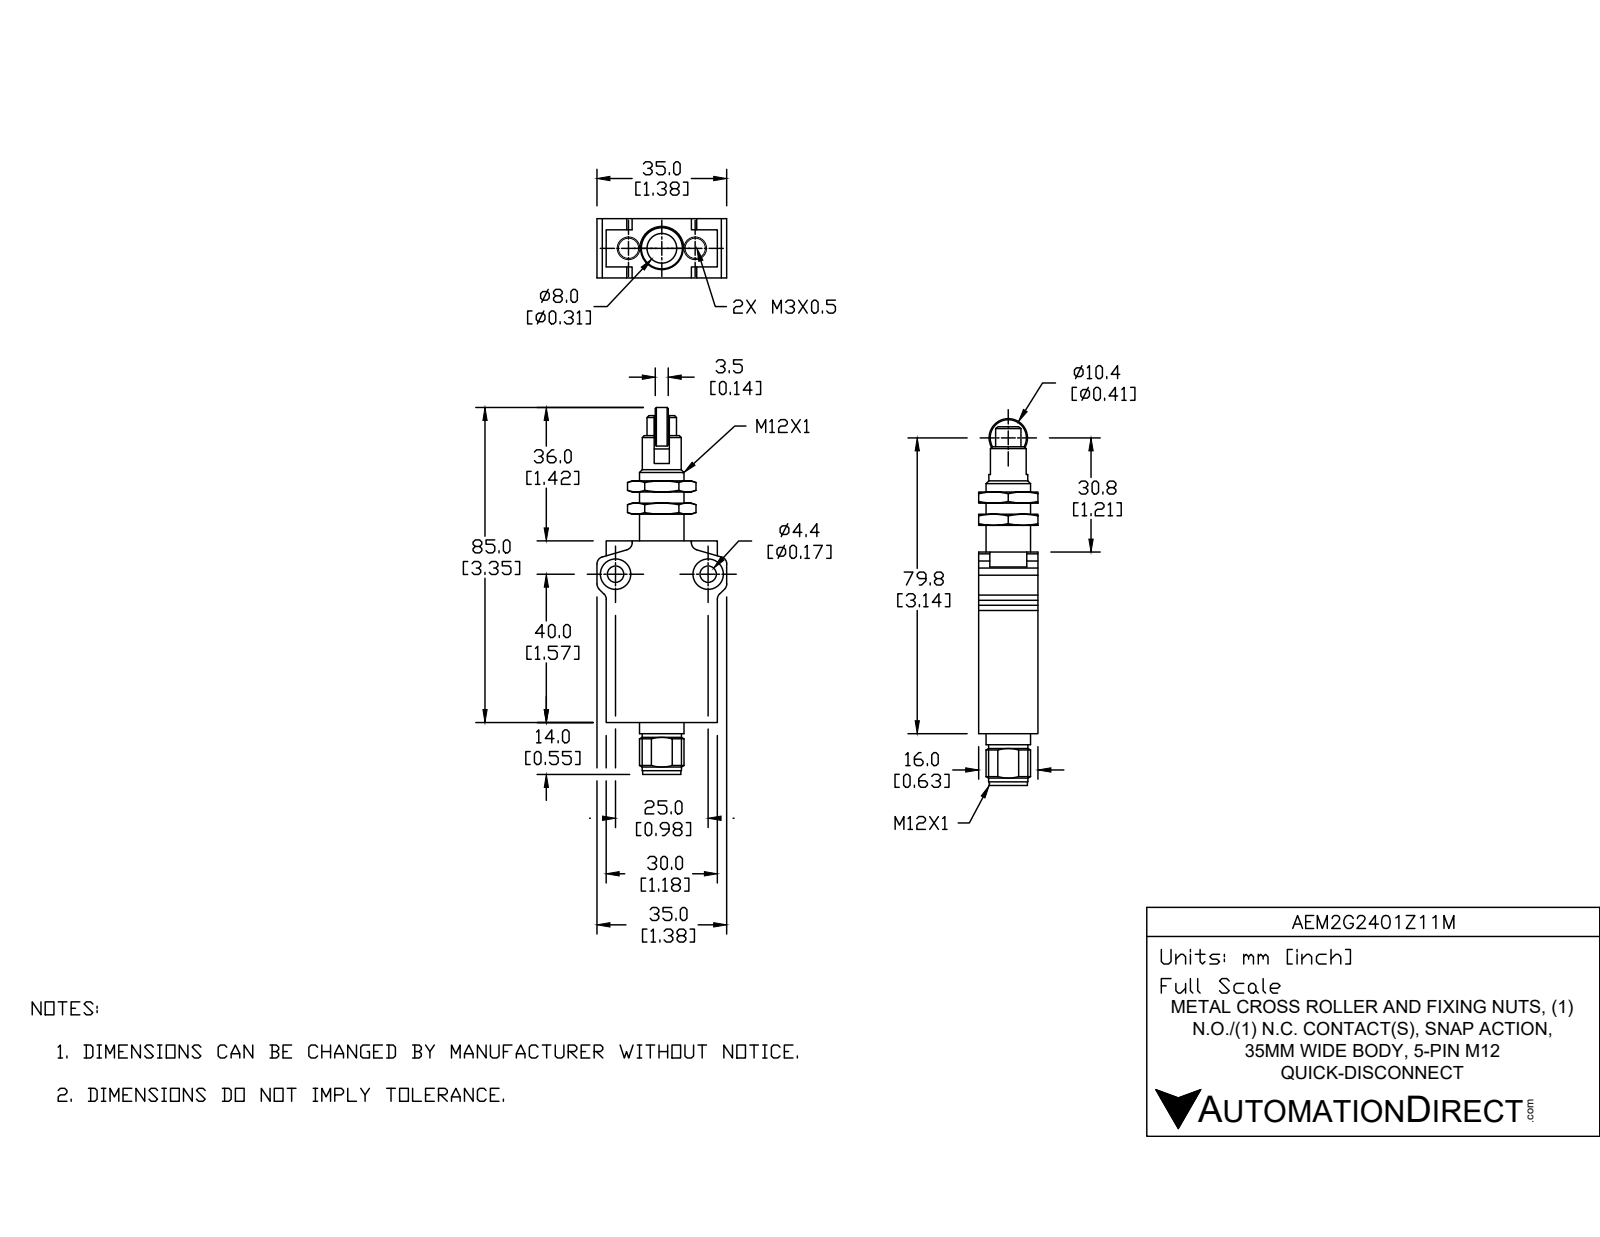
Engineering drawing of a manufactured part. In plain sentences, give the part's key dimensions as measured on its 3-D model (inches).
The part is named "AEM2G2401Z11M". Its 3-D file was written by "SolidWorks 2017 (AUTOMOTIVE_DESIGN)". It is 6 solids with 229 faces: 82 planar, 76 cylindrical and 71 other. Overall it measures 4.016 by 1.378 by 0.727 inches. Its volume is 1.785 cubic inches and its surface area 18.07 square inches. Round holes: 2 of diameter 0.118, 2 of diameter 0.173, 2 of diameter 0.323, 1 of diameter 0.317. Round bosses or shafts: 1 of diameter 0.472, 1 of diameter 0.417, 1 of diameter 0.413, 1 of diameter 0.409, 1 of diameter 0.406, 1 of diameter 0.313, 1 of diameter 0.22. Partial cylindrical surfaces (rounded edges, fillets, slot ends): 8 of radius 0.079, 1 of radius 0.256. The main face-to-face distances are 0.63, 1.181, 0.472, 0.118, 0.236, 2.047, 1.858, 0.189, 0.354, 0.157. The hole center spacings are 0.374, 0.748, 0.984.
